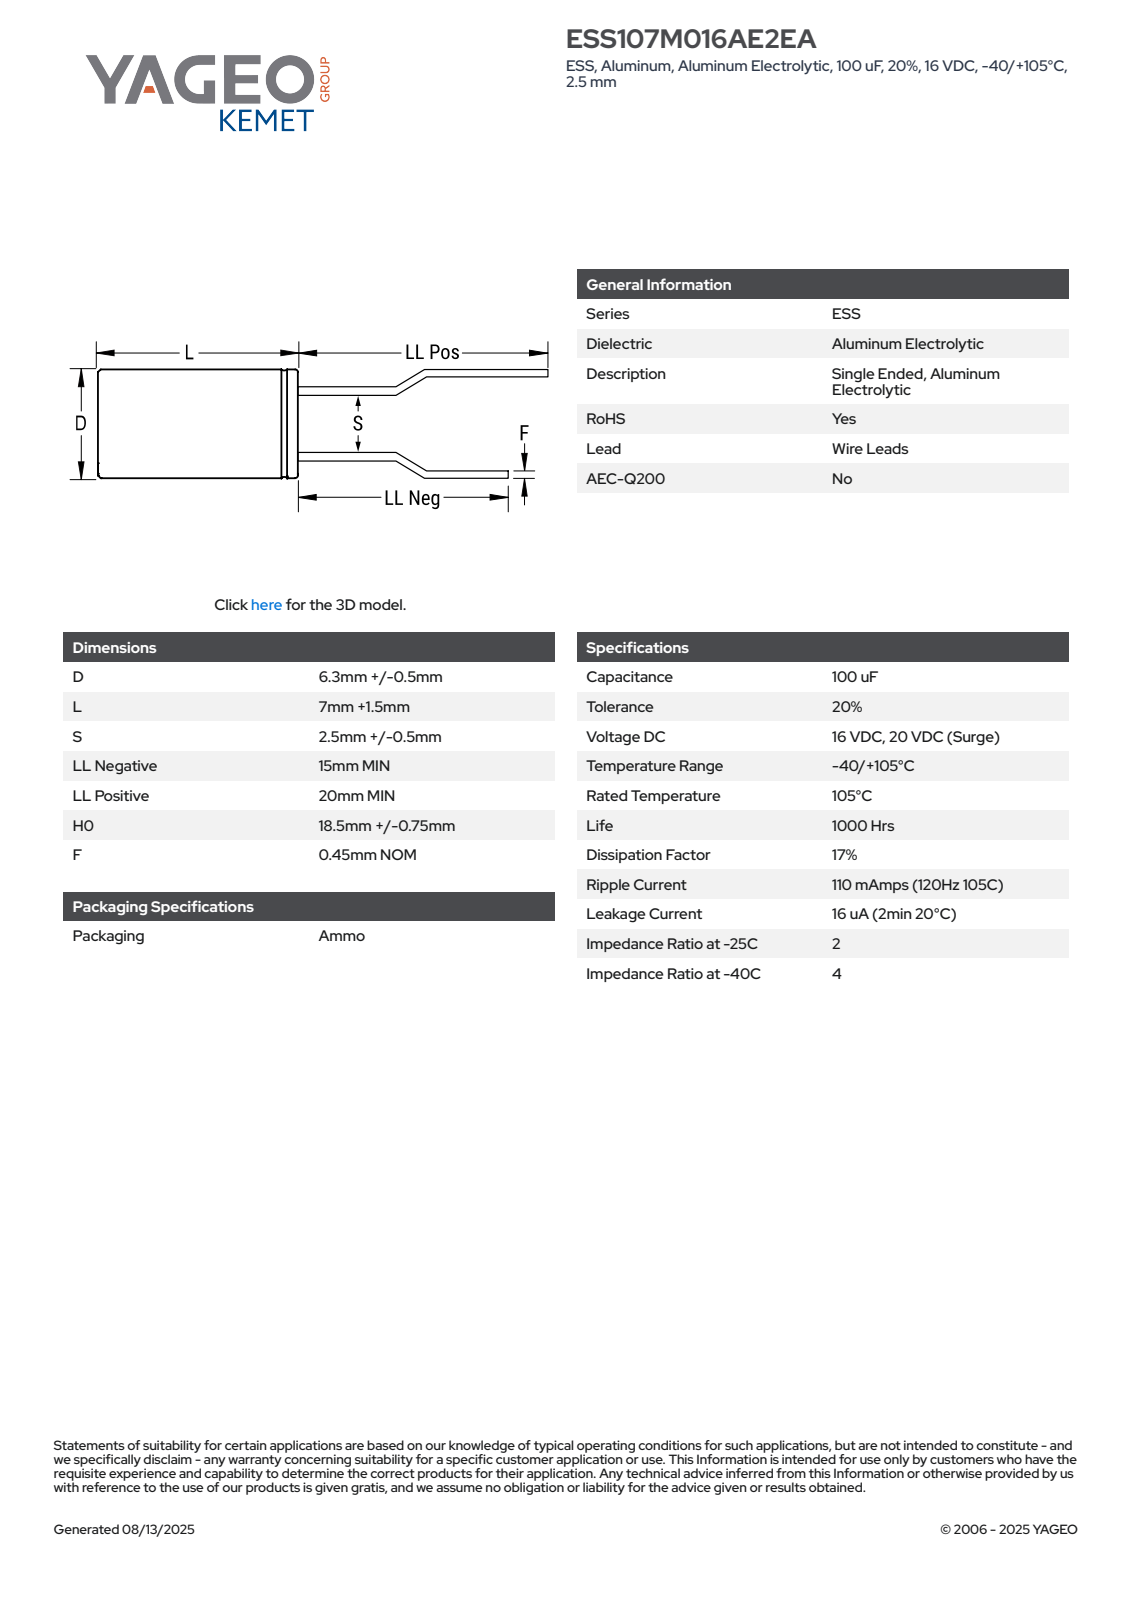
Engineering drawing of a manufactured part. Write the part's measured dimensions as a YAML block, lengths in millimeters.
part_name: "CAR_KTRS_6.3X7_D6.8L8.5S2.5F0.45"
step_written_by: "SolidWorks 2014 (AUTOMOTIVE_DESIGN)"
units: millimeters
bodies: {solids: 4, faces: 73, planar: 61, cylindrical: 8, other: 4}
overall_size: [28.5, 6.8, 6.8]
volume: 311
surface_area: 314
round_bosses_or_shafts:
  - {diameter: 0.45, count: 2}
  - {diameter: 6.8, count: 1}
face_to_face_distances: [8.5, 8.51, 23.51, 28.51, 23.5, 28.5, 15, 20, 5, 0.8]
